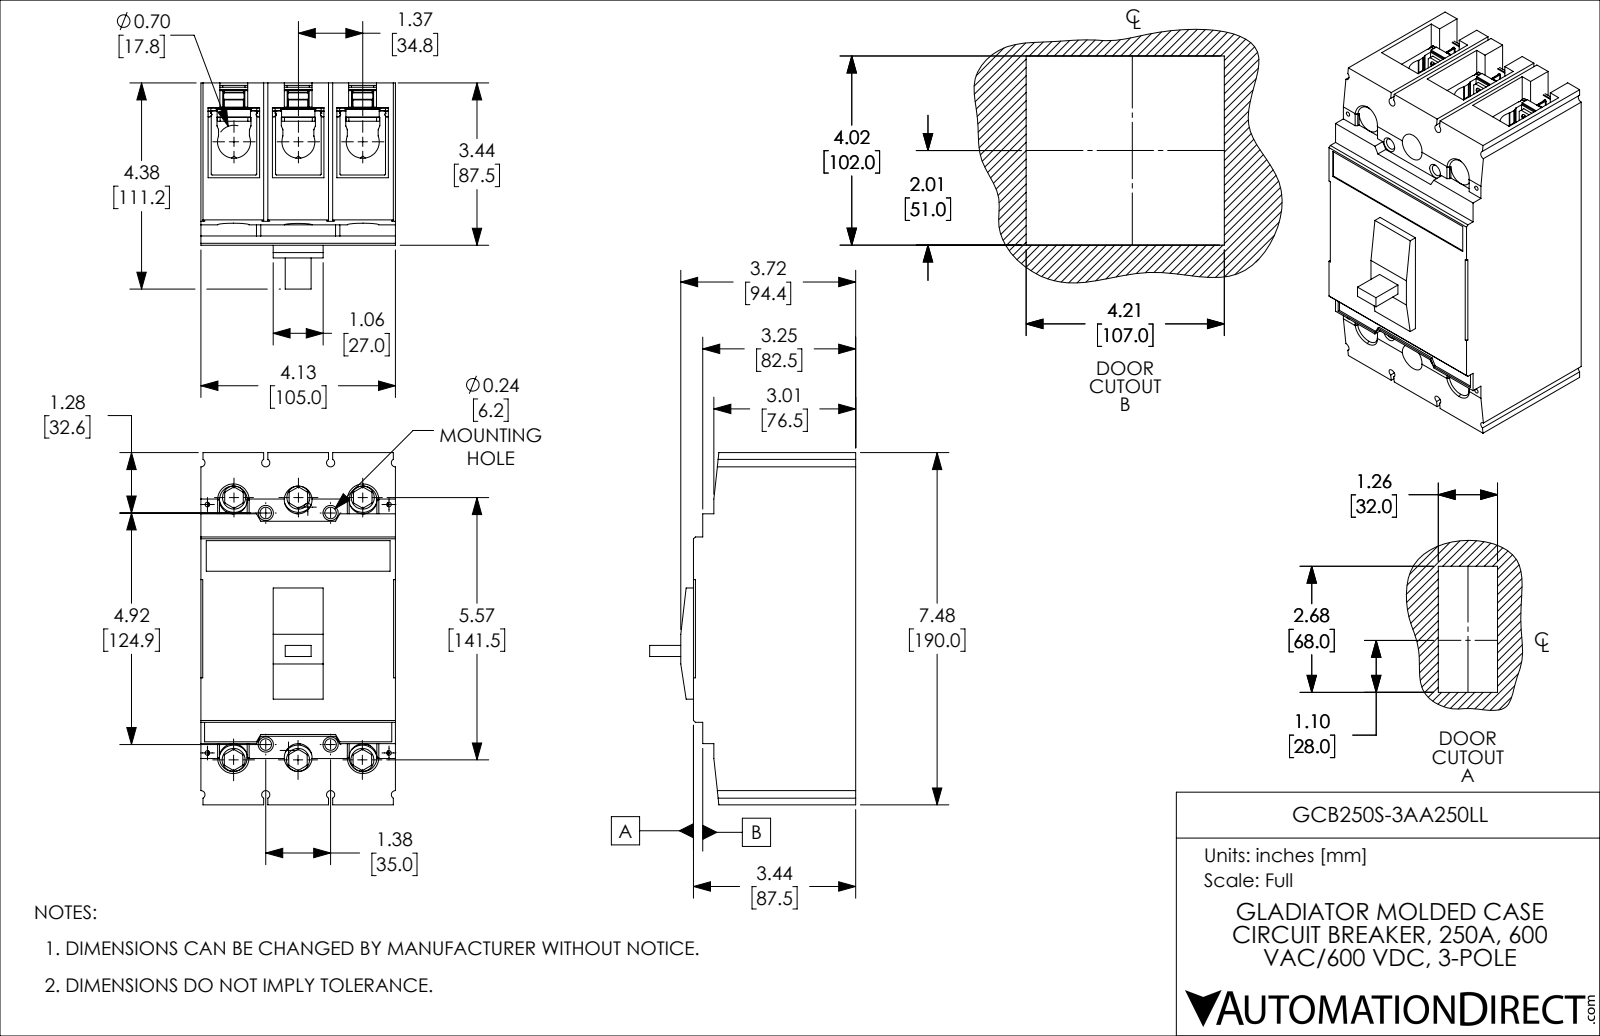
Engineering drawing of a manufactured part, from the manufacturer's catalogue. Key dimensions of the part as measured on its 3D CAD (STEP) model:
Part name (STEP PRODUCT): GCB250S-3AA250LL
STEP written by: SolidWorks 2021 (CONFIG_CONTROL_DESIGN)
Units: inches
Bodies: 25 solids, 2233 faces (975 planar, 958 cylindrical, 300 other)
Overall size (bounding box): 7.48 × 4.378 × 4.134
Volume: 87.11 in³ · Surface area: 315.7 in²
Round holes (diameter × count): ⌀0.067 ×24, ⌀0.157 ×24, ⌀0.098 ×10, ⌀0.354 ×6, ⌀0.591 ×6, ⌀0.689 ×6, ⌀0.173 ×4, ⌀0.244 ×4
Round bosses / shafts (diameter × count): ⌀0.709 ×6
Partial cylindrical surfaces — rounded edges, fillets, slot ends (radius × count): R0.012 ×206, R0.039 ×72, R0.059 ×36, R0.02 ×26, R0.008 ×24, R0.079 ×20, R0.016 ×12, R0.031 ×12
Main face-to-face distances: 1.368, 4.134, 2.736, 1.094, 0.843, 0.252, 0.059, 1.378, 6.102, 3.445
Hole centre spacings: 0.285, 0.743, 1.046, 1.378, 5.24, 6.298, 1.368, 1.426
